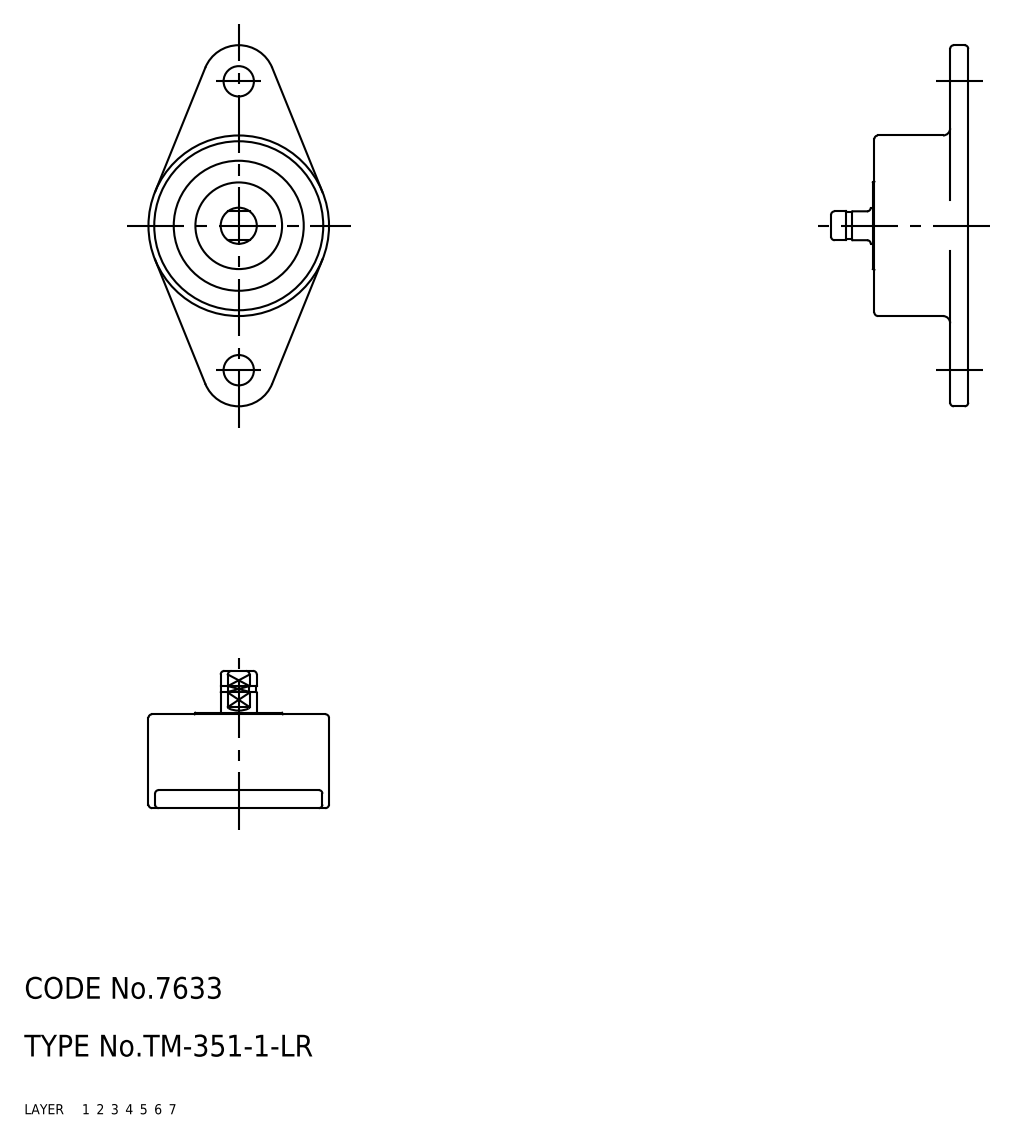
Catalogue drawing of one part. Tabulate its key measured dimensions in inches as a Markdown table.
| quantity | value |
| --- | --- |
| part name | TM_351_0_5_LR |
| STEP written by | SolidWorks 2015 (AUTOMOTIVE_DESIGN) |
| units | inches |
| bodies | 0 solids, 59 faces (18 planar, 26 cylindrical, 15 other) |
| overall size | 1.969 × 0.984 × 0.748 |
| round holes (diameter × count) | 0.165 × 2 |
| round bosses / shafts (diameter × count) | 0.984 × 1, 0.197 × 1 |
| partial cylindrical surfaces (radius × count) | 0.02 × 8, 0.197 × 2, 0.094 × 1 |
| main face-to-face distances | 0.512, 0.098, 0.413, 0.52, 0.421, 0.984, 0.157, 0.748, 0.65, 0.236 |
| hole center spacings | 1.575 |
